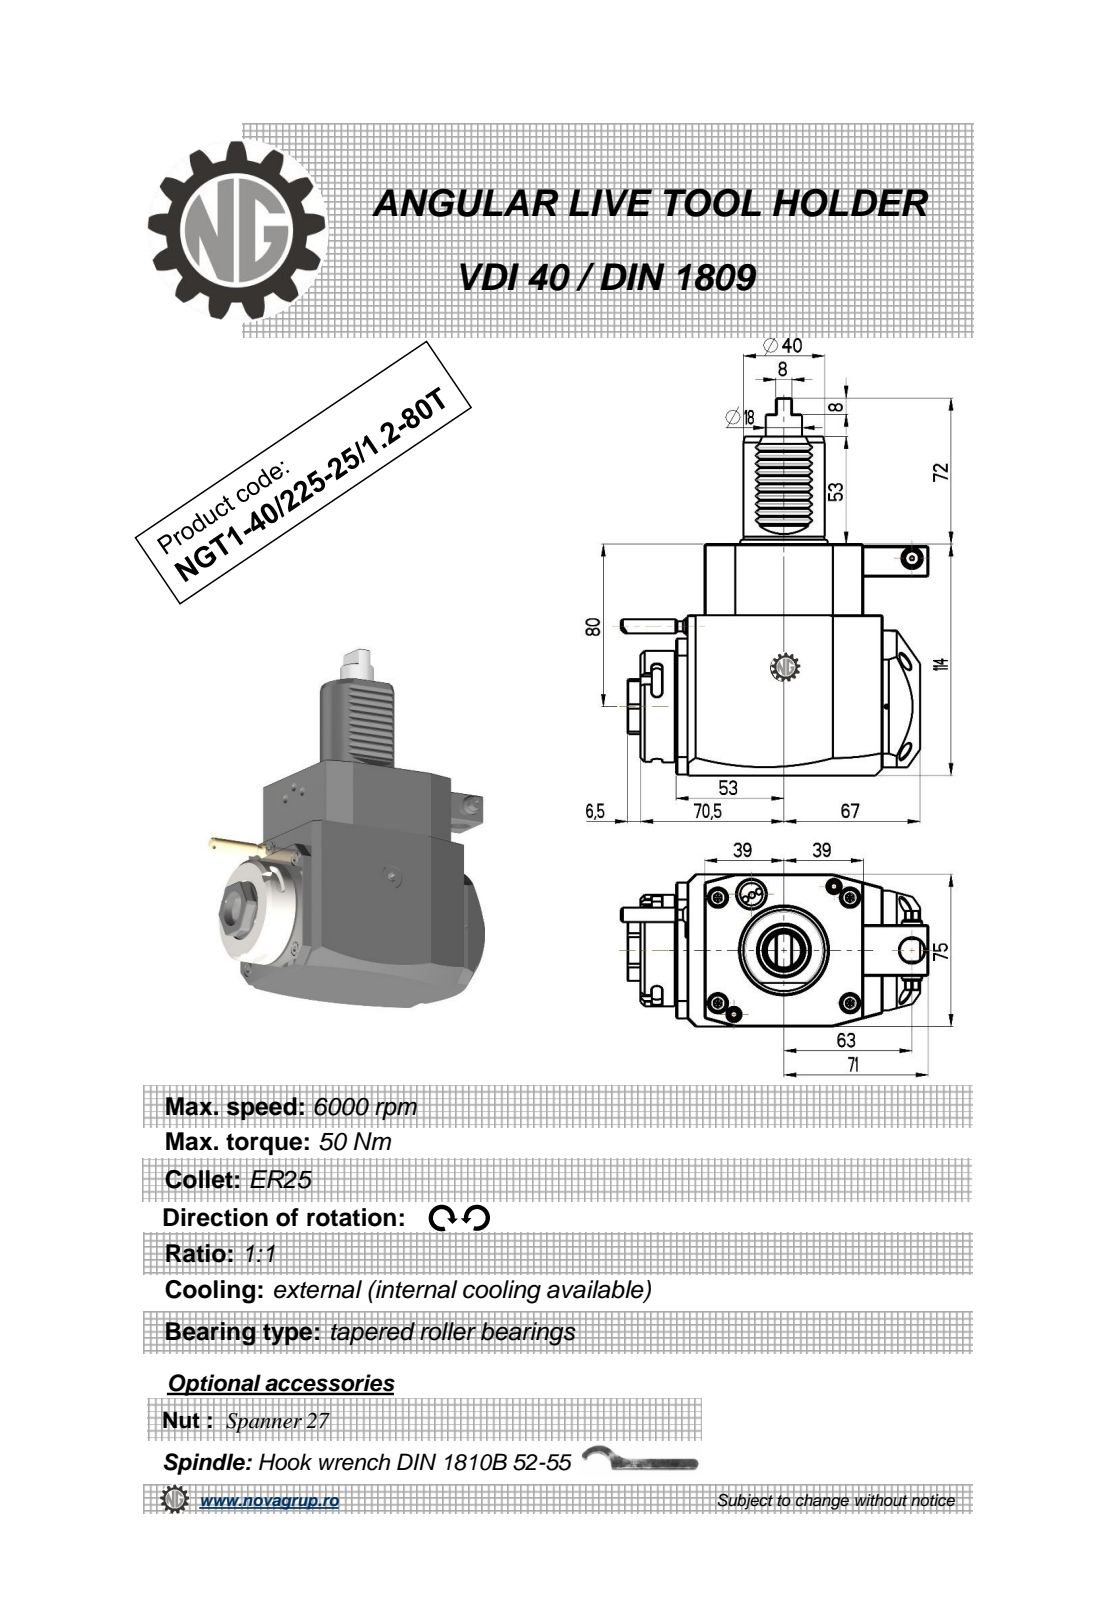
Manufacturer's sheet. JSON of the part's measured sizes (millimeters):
{"part_name": "NGT1_40_225_25_1_2_80T", "step_written_by": "PRO/ENGINEER BY PARAMETRIC TECHNOLOGY CORPORATION, 2010280 (CONFIG_CONTROL_DESIGN)", "units": "millimeters", "bodies": {"solids": 1, "faces": 274, "planar": 166, "cylindrical": 62, "other": 46}, "overall_size": [186, 151.33, 75], "volume_mm3": 954148, "surface_area_mm2": 68979, "round_bosses_or_shafts": [[55, 1], [48, 1], [40, 1], [17.8, 1], [10, 1], [8, 1], [7, 1], [5, 1]], "partial_cylinders_radius": [[0.3, 10], [2.5, 6], [0.8, 2], [180, 2], [0.5, 1], [3.85, 1], [15, 1], [24.5, 1]], "face_to_face_distances": [75, 114, 14, 92, 78, 17.5, 4, 31.5, 35, 120]}
